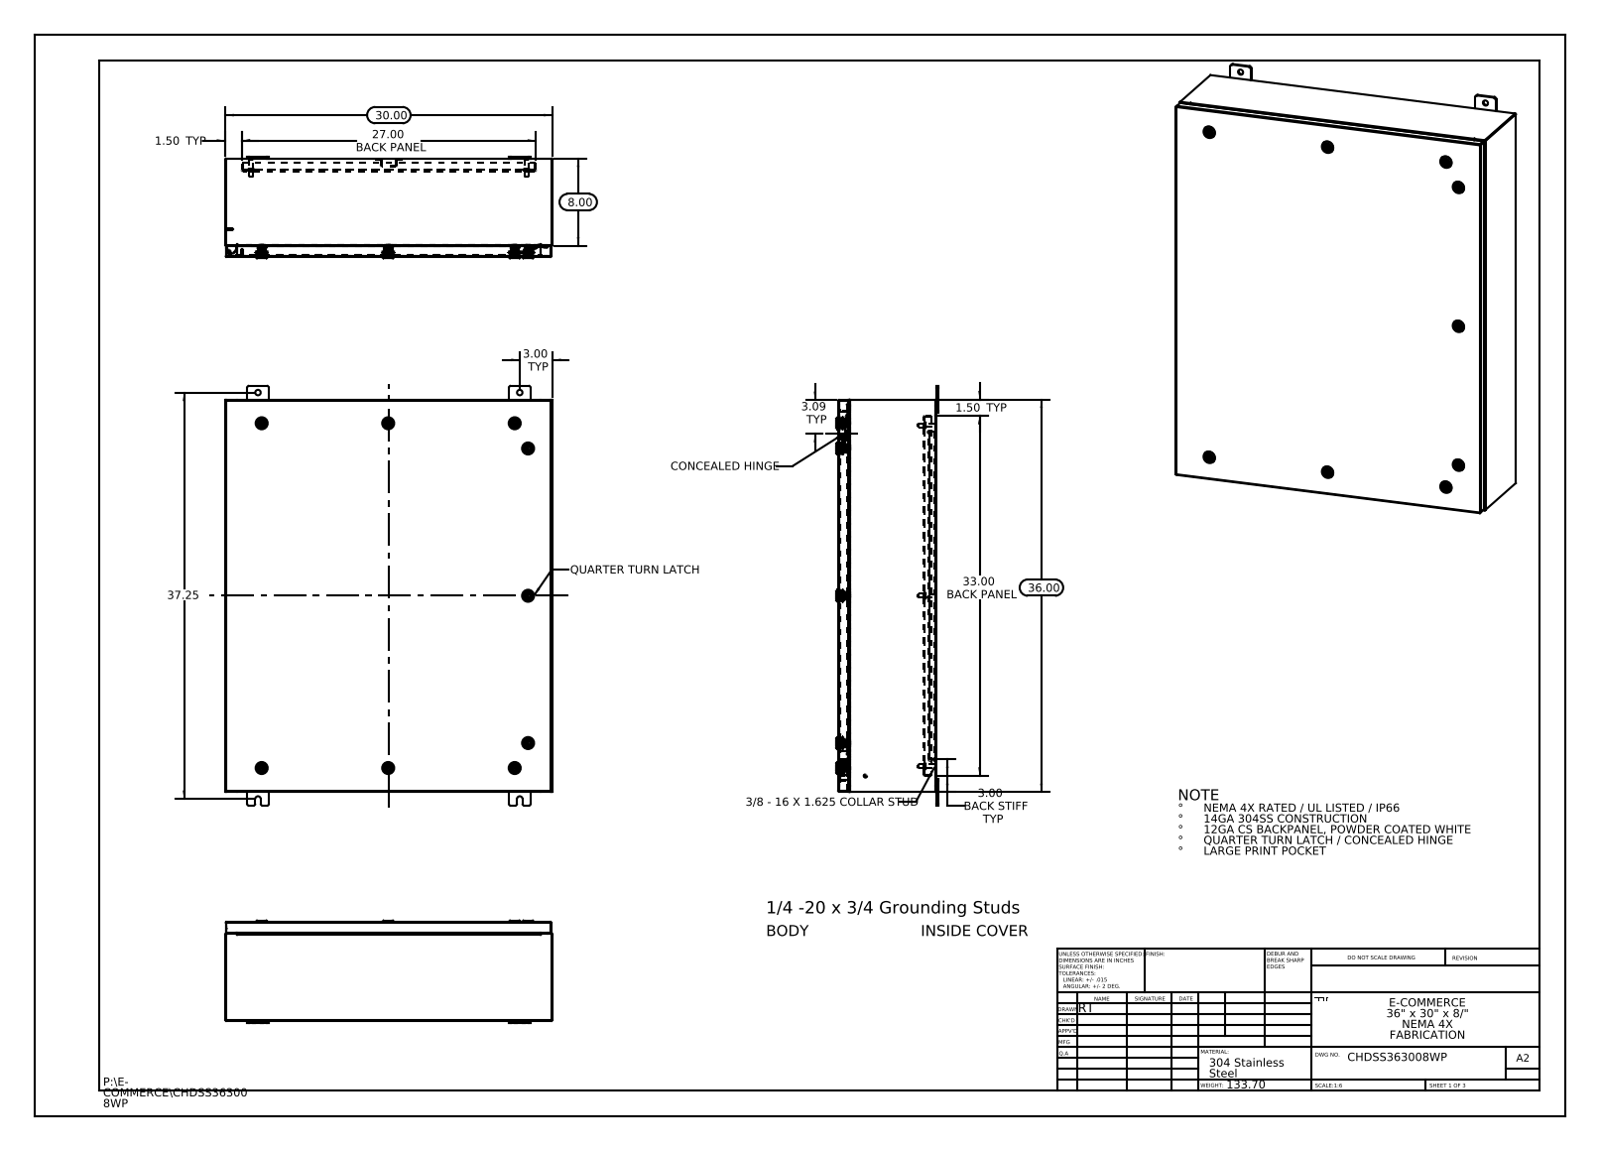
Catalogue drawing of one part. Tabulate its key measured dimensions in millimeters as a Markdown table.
| quantity | value |
| --- | --- |
| part name | Quarter-20 CD Stud; CHDSS363008WP Bottom; Insert-221320-IB-Industrilas_Insert-221320-IB-Industrilas; CHDSS363008WP Mounting Feet (+8 more) |
| STEP written by | SolidWorks 2013 (CONFIG_CONTROL_DESIGN) |
| units | millimeters |
| bodies | 76 solids, 8024 faces (2316 planar, 2506 cylindrical, 3202 other) |
| overall size | 977.9 × 762 × 237.6 |
| volume | 7 741 000 mm³ |
| surface area | 7 659 000 mm² |
| round holes (diameter × count) | 12.7 × 10, 5 × 9, 10 × 9, 10.2 × 9, 16 × 9, 20 × 9, 3.5 × 4, 5.4 × 1 |
| round bosses / shafts (diameter × count) | 6 × 11, 28 × 9, 19.8 × 9, 15.9 × 9, 15.5 × 9, 13.5 × 9, 10 × 9, 2.9 × 9 |
| partial cylindrical surfaces (radius × count) | 0.2 × 297, 3 × 297, 0.7 × 108, 0.5 × 36, 5 × 36, 0.3 × 26, 4.8 × 24, 2.2 × 22 |
| main face-to-face distances | 1.9, 1.9, 225.1, 226.9, 227, 228.9, 2.6, 25.4, 27.3, 199.7 |
| hole center spacings | 294.6, 396.9, 754.2, 855, 641.4, 802.6, 47.2, 54.1 |
